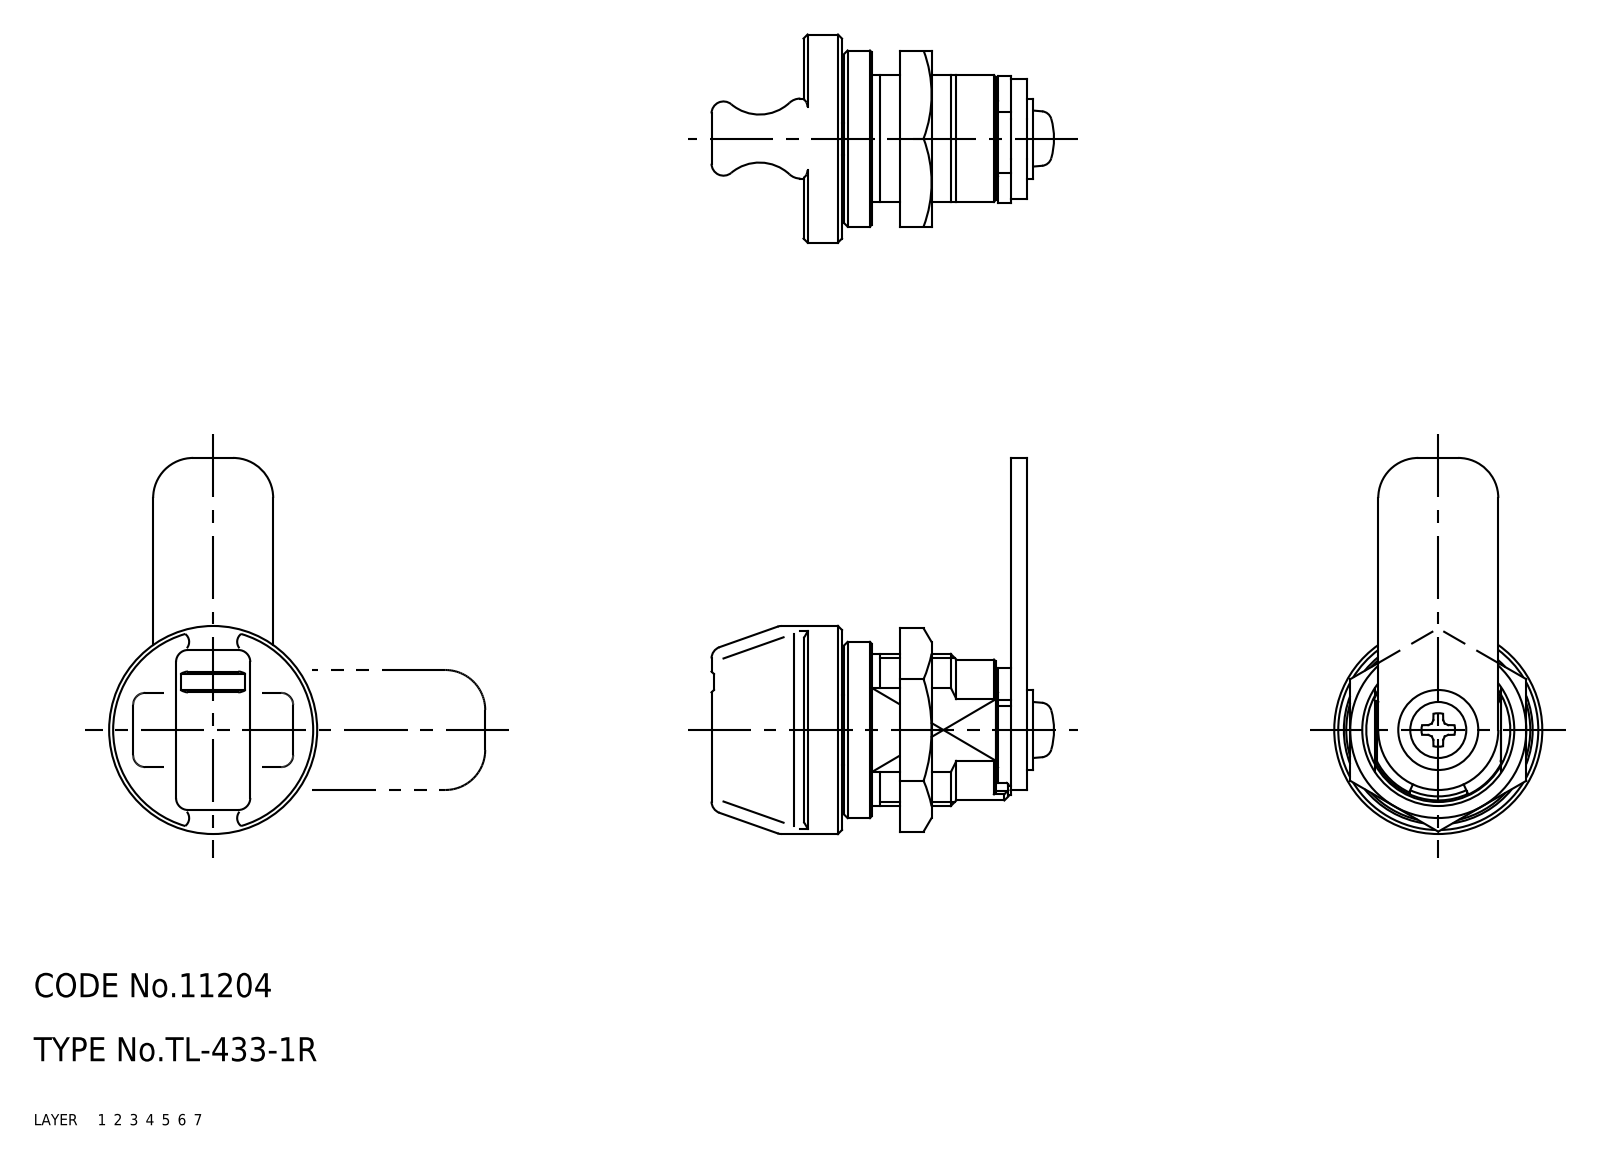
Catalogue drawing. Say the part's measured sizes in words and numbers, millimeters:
The part is named "X2_6B62308191D15177_X0; X2_5E735EA791D1_X0_(_X2_547C3073_X0_4); TL_433_1R; X2_53415B577A744ED8304D30BF30C330D430F3306D3058_X0_(_X2_547C3073_X0_4) (+3 more)". Its 3-D file was written by "SolidWorks 2015 (AUTOMOTIVE_DESIGN)". It is 6 solids with 223 faces: 86 planar, 73 cylindrical and 64 other. Overall it measures 47 by 42.8 by 26 millimeters. Its volume is 10 781 cubic millimeters and its surface area 7 224 square millimeters. Round holes: 1 of diameter 3.45, 1 of diameter 4.3, 1 of diameter 18.4, 1 of diameter 23. Round bosses or shafts: 1 of diameter 26, 1 of diameter 22, 1 of diameter 10, 1 of diameter 9.8, 1 of diameter 4, 1 of diameter 3.2. Partial cylindrical surfaces (rounded edges, fillets, slot ends): 8 of radius 1.5, 4 of radius 0.5, 2 of radius 2, 2 of radius 5, 2 of radius 5.5, 1 of radius 3.5, 1 of radius 3.6, 1 of radius 4.7. The main face-to-face distances are 2, 24.3, 1.6, 26.3, 20.9, 3.4, 22.9, 5, 15.8, 25.9.
